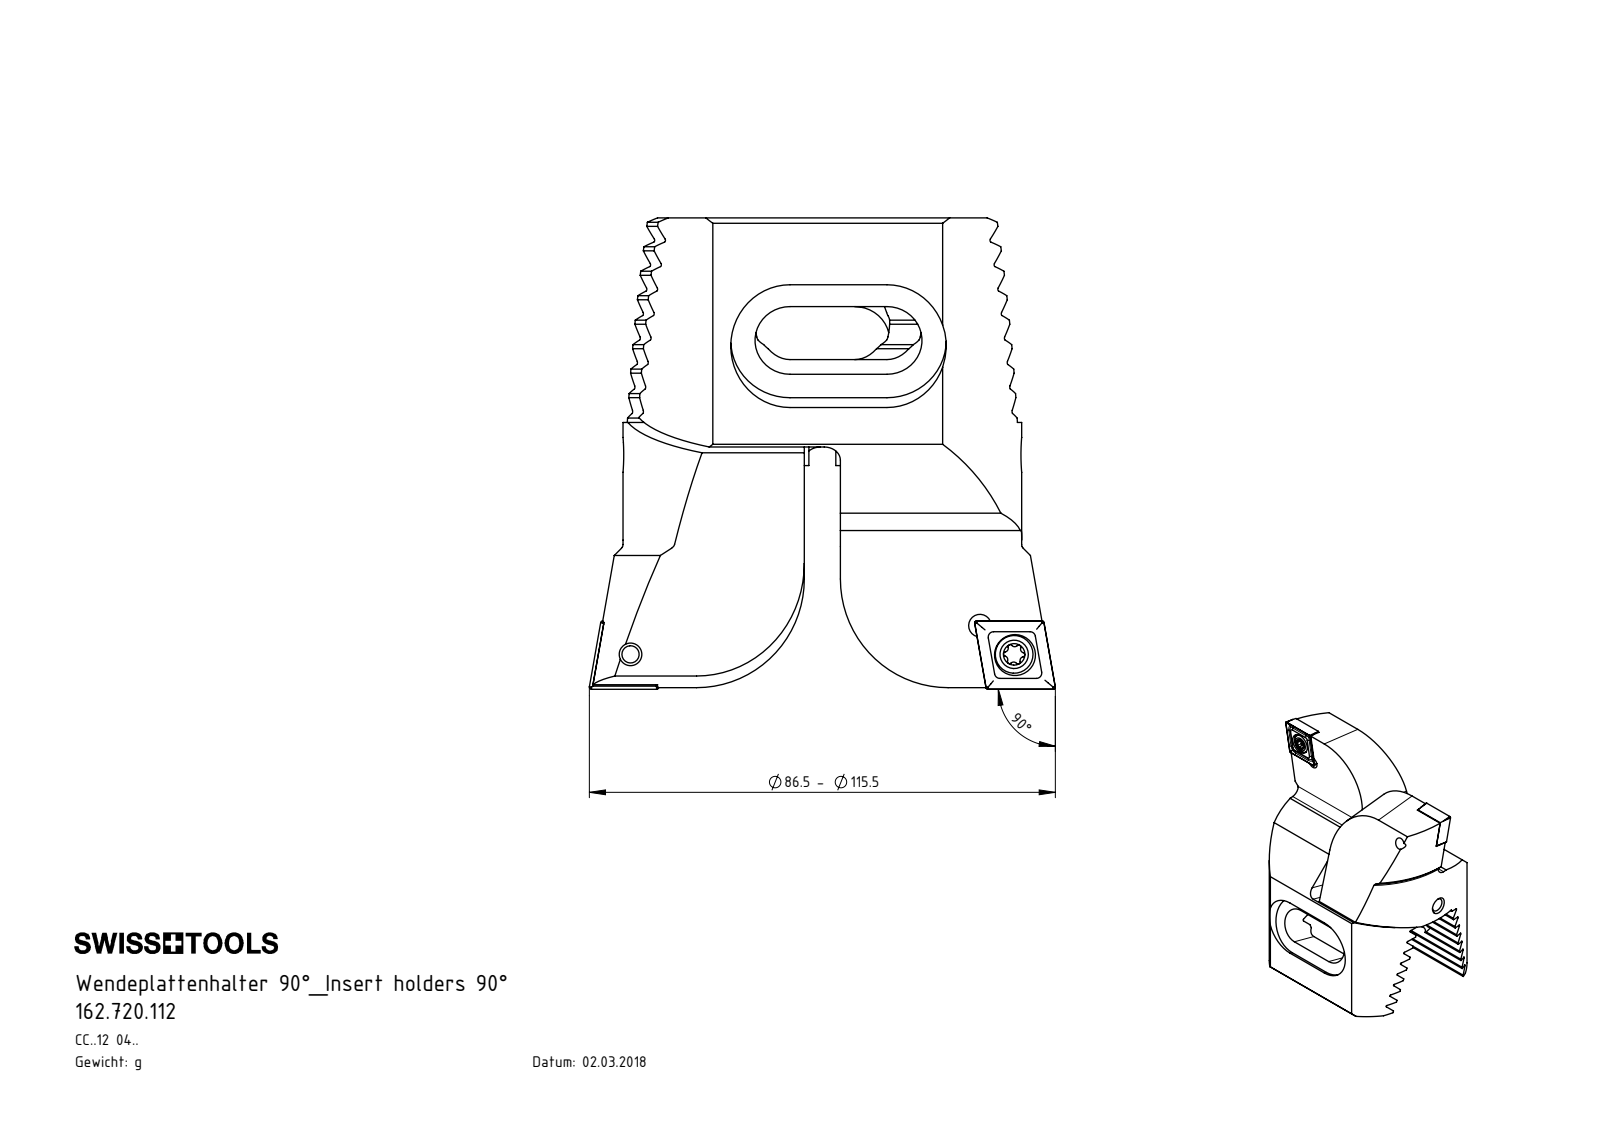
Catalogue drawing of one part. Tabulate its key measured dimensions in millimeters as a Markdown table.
| quantity | value |
| --- | --- |
| part name | 162.720.112; Z72-WCC.001.050_A; WCC-ER2.001.010_A; Z72-ER3.001.030 (+1 more) |
| STEP written by | SolidWorks 2017 (CONFIG_CONTROL_DESIGN) |
| units | millimeters |
| bodies | 8 solids, 434 faces (178 planar, 142 cylindrical, 114 other) |
| overall size | 87.45 × 86.5 × 58 |
| volume | 146 270 mm³ |
| surface area | 38 167 mm² |
| round holes (diameter × count) | 4.2 × 4, 1 × 2, 5.5 × 2, 7.6 × 2, 5 × 1 |
| round bosses / shafts (diameter × count) | 7 × 2, 5 × 2, 6 × 1, 4 × 1 |
| partial cylindrical surfaces (radius × count) | 0.34 × 16, 0.39 × 12, 0.69 × 8, 1 × 8, 0.69 × 4, 3 × 4, 6.5 × 4, 11 × 4 |
| main face-to-face distances | 4.07, 8.14, 12.21, 16.28, 28.7, 29.3, 24.43, 0.91, 20.36, 58 |
| hole center spacings | 8.3, 8.5, 15, 65.08, 65.24, 71.37, 28.98, 58.5 |
